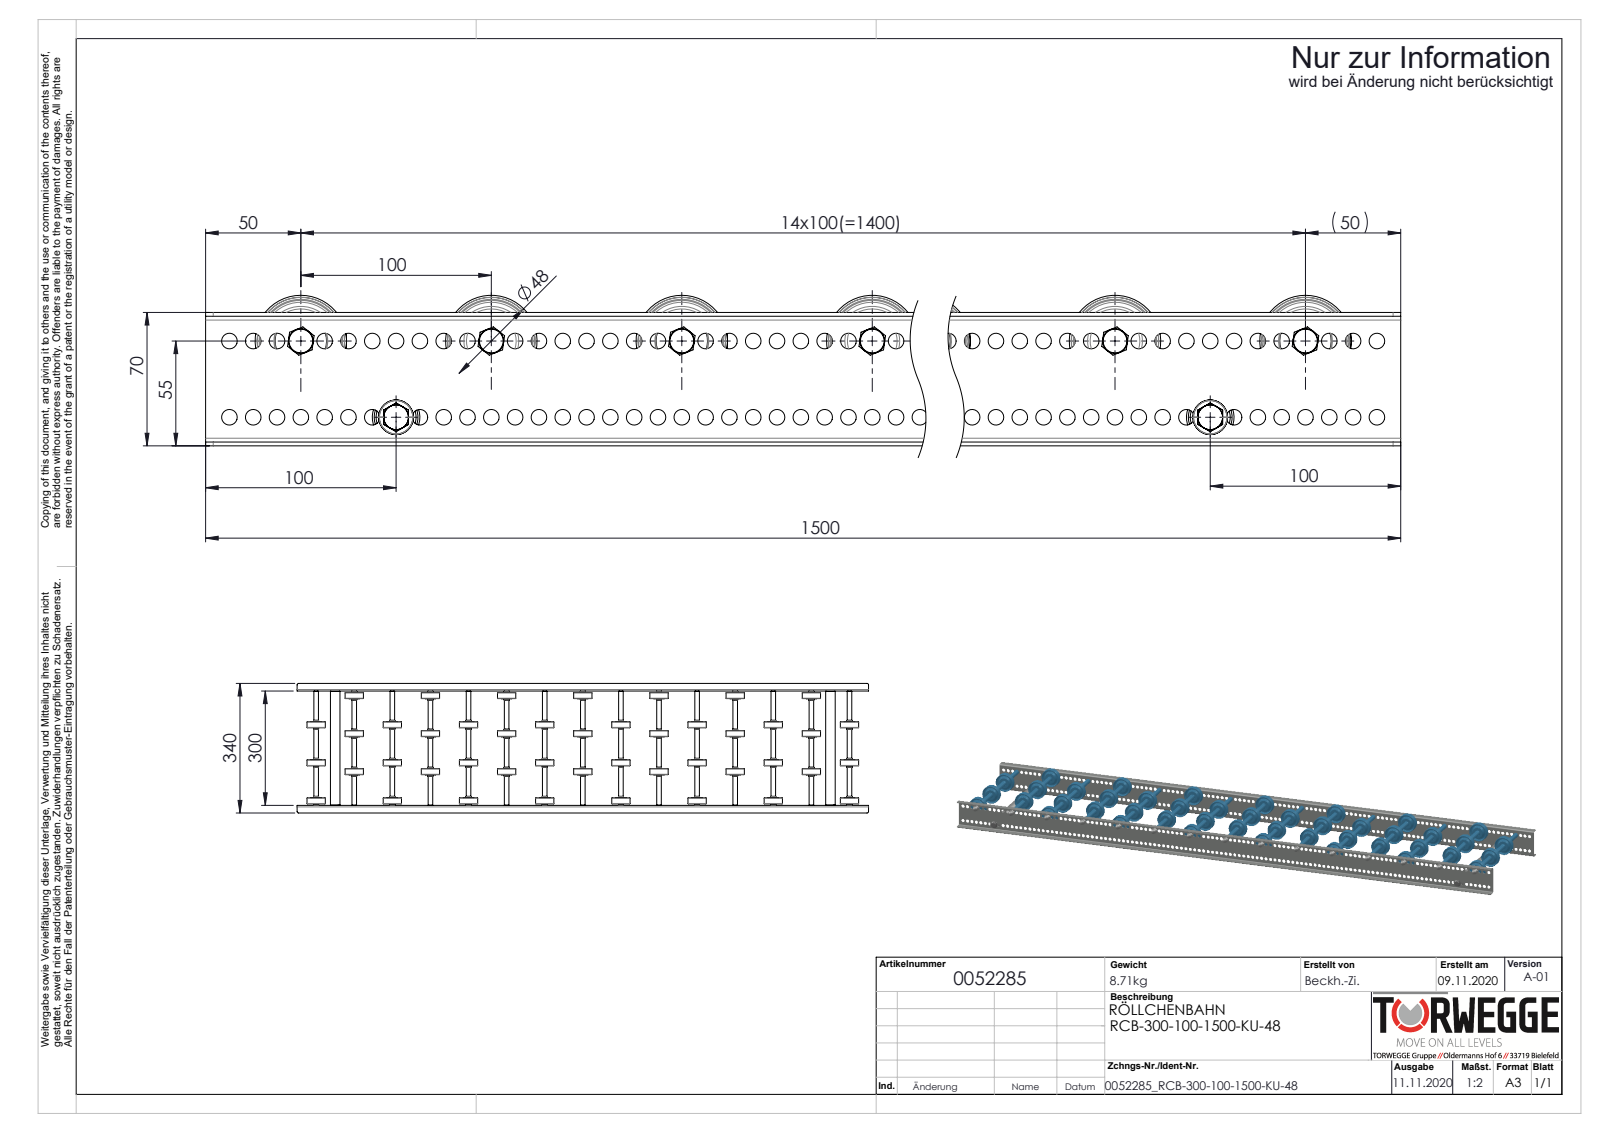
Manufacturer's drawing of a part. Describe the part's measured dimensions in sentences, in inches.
The part is named "Röllchenachse-für-Konfiguration_EL300; Traversen_KFG_L300; Hutmutter_DIN_1587_M8; 0011532_2300-48-8 (+5 more)". Its 3-D file was written by "SolidWorks 2020 (AUTOMOTIVE_DESIGN)". It is 147 solids with 5567 faces: 975 planar, 2148 cylindrical and 2444 other. Overall it measures 59.055 by 13.386 by 3.11 inches. Its volume is 119.1 cubic inches and its surface area 2 362 square inches. Round holes: 238 of diameter 0.323, 15 of diameter 0.262, 15 of diameter 0.38, 15 of diameter 0.539, 2 of diameter 0.268, 2 of diameter 0.827. Round bosses or shafts: 17 of diameter 0.315, 15 of diameter 1.89, 15 of diameter 1.063, 15 of diameter 0.5, 15 of diameter 0.492, 15 of diameter 0.472, 2 of diameter 0.984. Partial cylindrical surfaces (rounded edges, fillets, slot ends): 8 of radius 0.157, 4 of radius 0.079. The main face-to-face distances are 0.079, 11.89, 2.677, 11.969, 11.811, 2.756, 2.598, 3.929, 0.642, 2.996. The hole center spacings are 0.492, 0.984, 1.476, 1.969, 2.461, 2.953, 3.445, 3.937.
